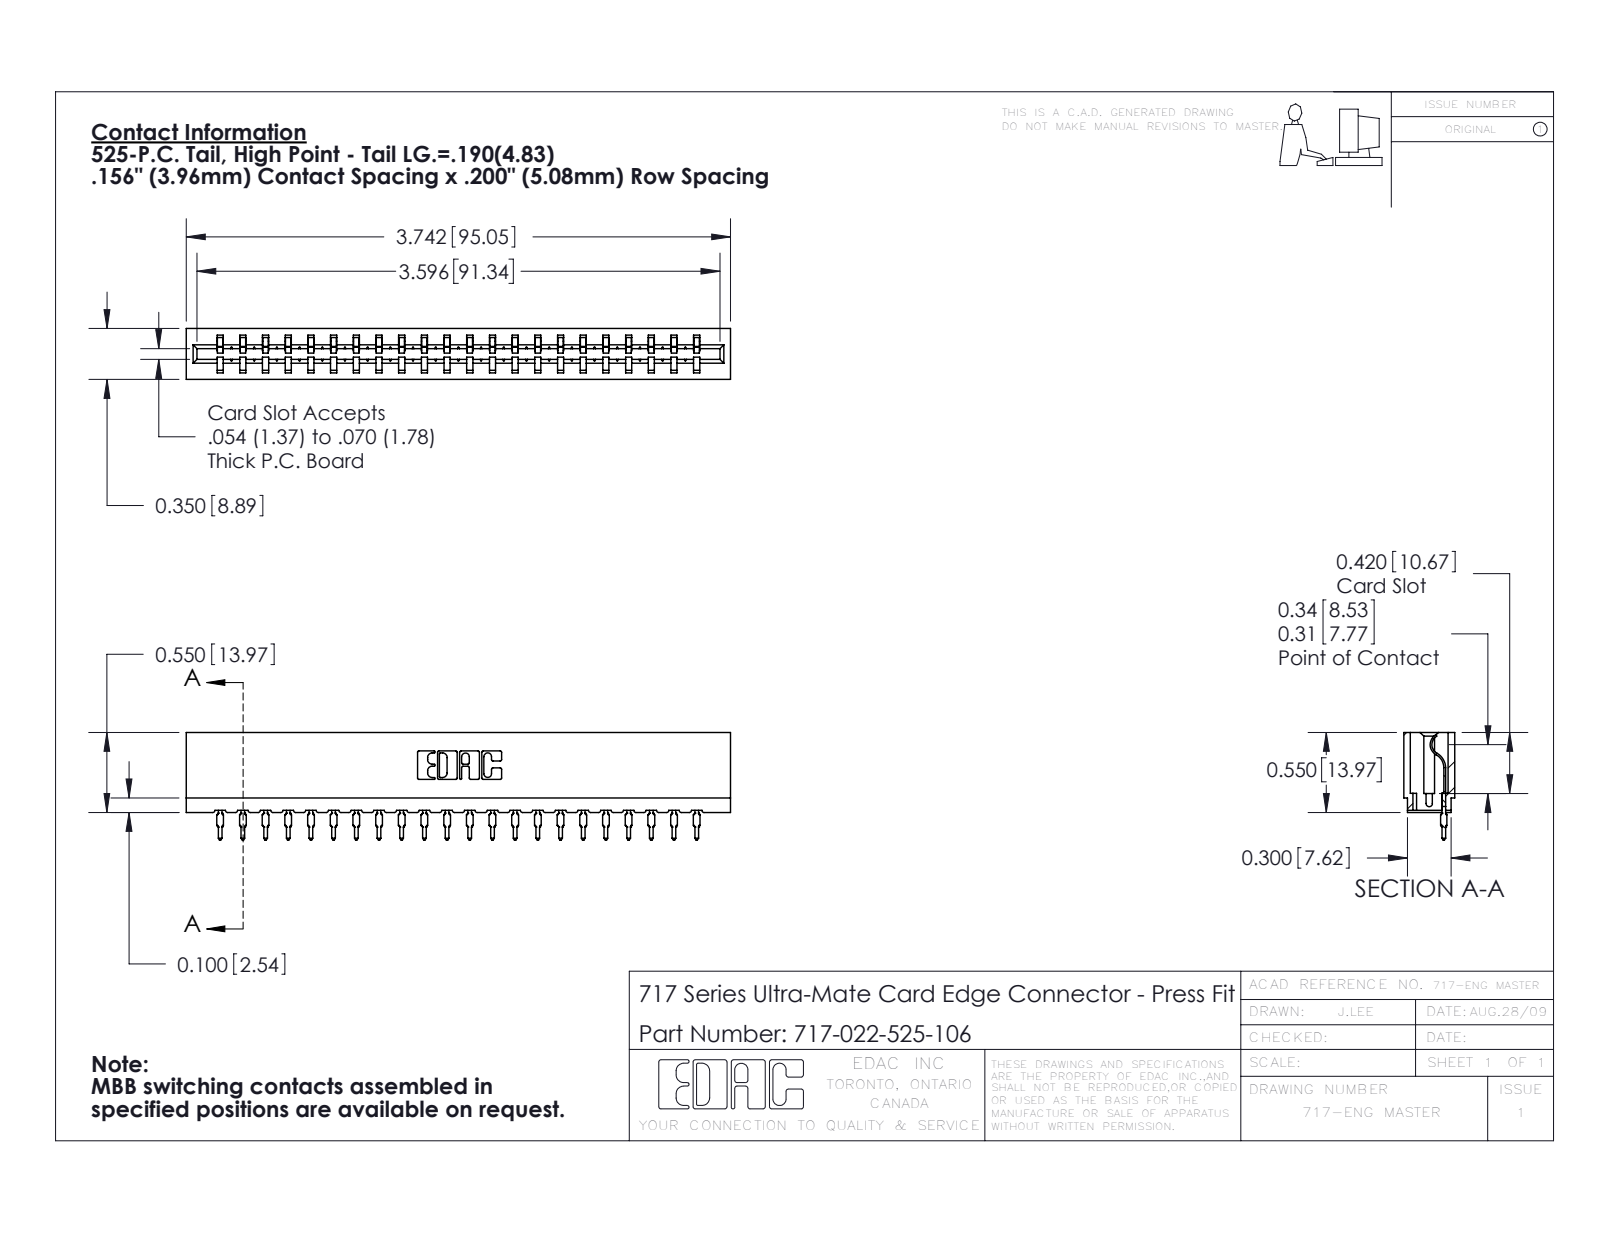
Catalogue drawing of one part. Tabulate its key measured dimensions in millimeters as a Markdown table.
| quantity | value |
| --- | --- |
| part name | 717-022-525-106; 745-292-001_525; 717 Part_Insulator Option - 06 |
| STEP written by | SolidWorks 2016 (CONFIG_CONTROL_DESIGN) |
| units | millimeters |
| bodies | 23 solids, 2580 faces (1550 planar, 458 cylindrical, 572 other) |
| overall size | 95 × 18.8 × 8.9 |
| volume | 8 100 mm³ |
| surface area | 11 090 mm² |
| partial cylindrical surfaces (radius × count) | 0.4 × 44, 0.5 × 44, 0.3 × 22, 0.2 × 6, 0.8 × 6, 0.1 × 4, 0.3 × 4, 0.7 × 3 |
| main face-to-face distances | 5.4, 3.5, 8.9, 4, 1.9, 15.8, 0.6, 1.1, 7.7, 2.4 |
